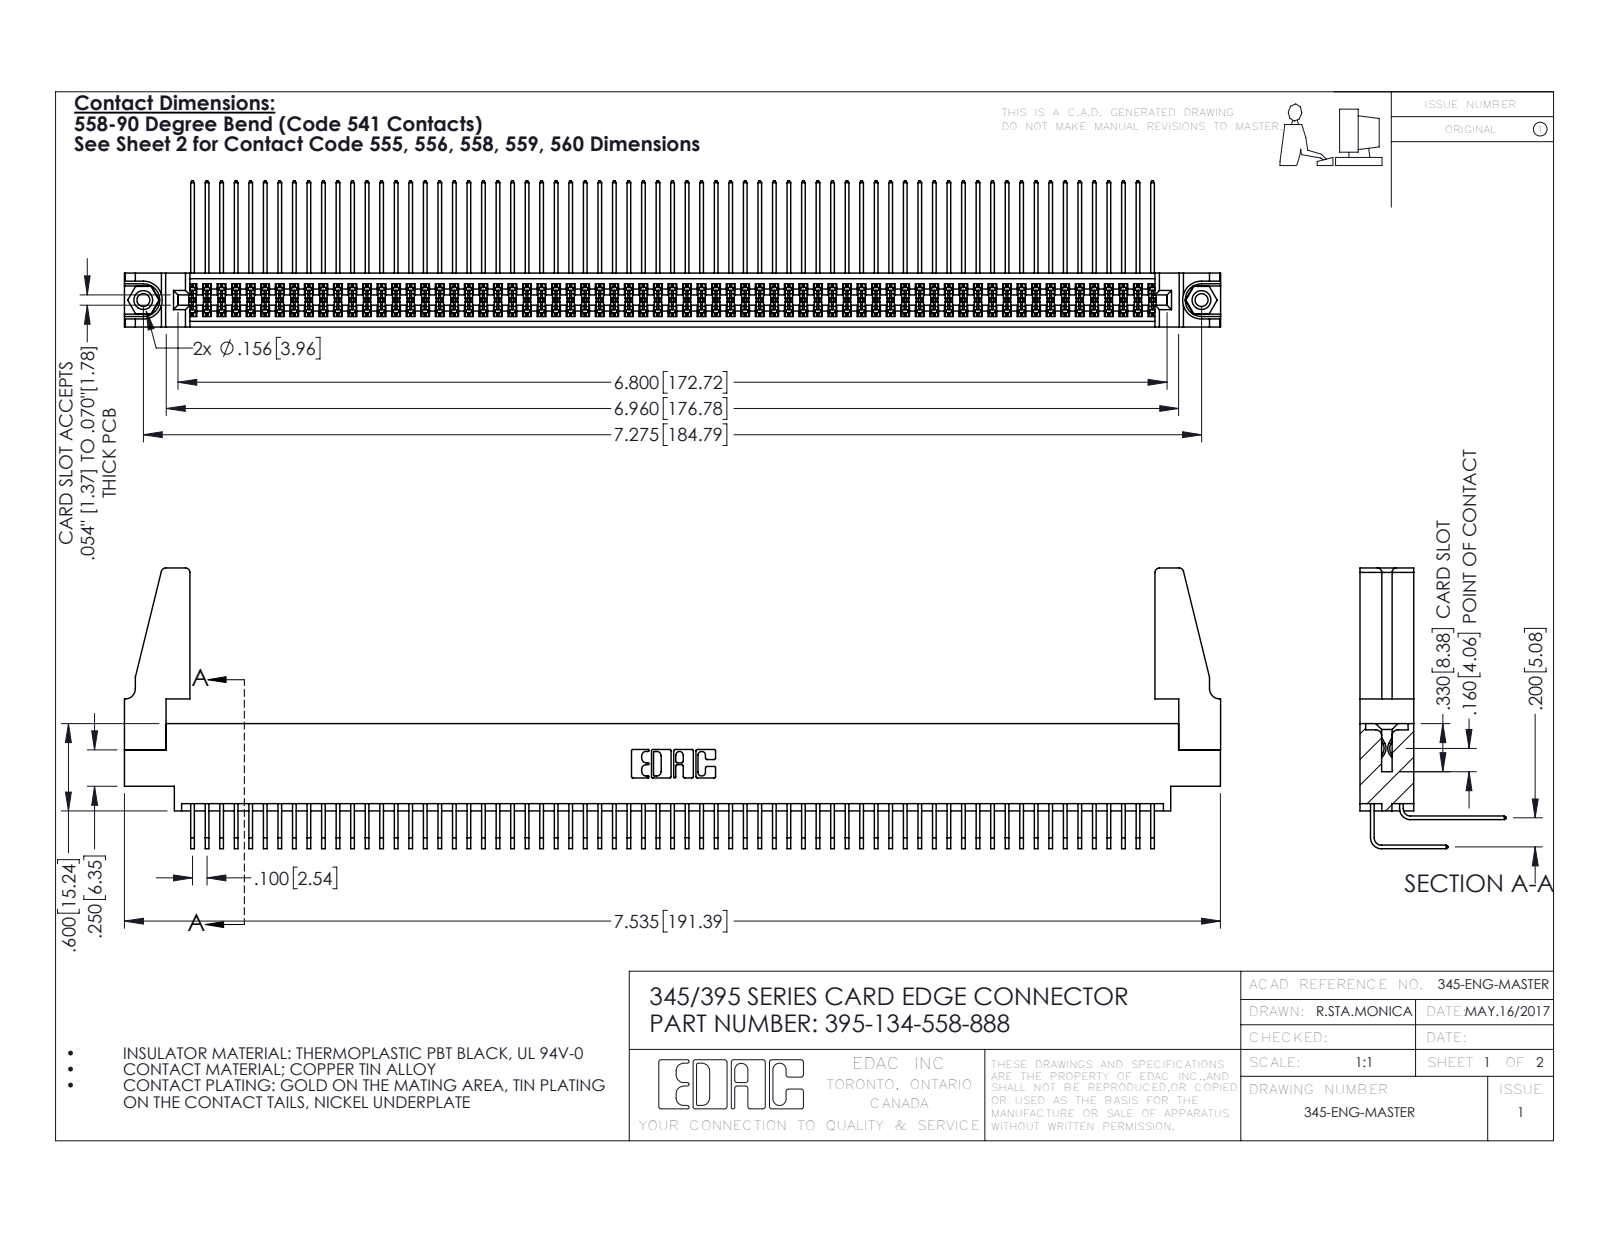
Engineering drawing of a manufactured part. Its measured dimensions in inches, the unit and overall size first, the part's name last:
Units: inches
Overall size (bounding box): 7.536 × 1.929 × 1.005
Round holes (diameter × count): ⌀0.089 ×2, ⌀0.125 ×2, ⌀0.156 ×2, ⌀0.064 ×1
Round bosses / shafts (diameter × count): ⌀0.155 ×2
Partial cylindrical surfaces — rounded edges, fillets, slot ends (radius × count): R0.006 ×202, R0.01 ×22, R0.03 ×8, R0.007 ×6, R0.031 ×6, R0.026 ×3, R0.014 ×2, R0.019 ×2
Main face-to-face distances: 0.072, 0.298, 0.2, 0.37, 0.098, 0.272, 0.025, 0.225, 0.175, 0.025
Hole centre spacings: 0.27, 7.039, 7.275
Volume: 1.388 in³ · Surface area: 56.09 in²
Bodies: 139 solids, 7222 faces (4846 planar, 2360 cylindrical, 16 other)
Part name (STEP PRODUCT): 345 Part_0.170 Offset - 0.156 Dia-TH; 345-250-001_345-250-001-102; 395-134-558-888; 345-220-078_345-220-088 (+2 more)
STEP written by: SolidWorks 2016 (CONFIG_CONTROL_DESIGN)
